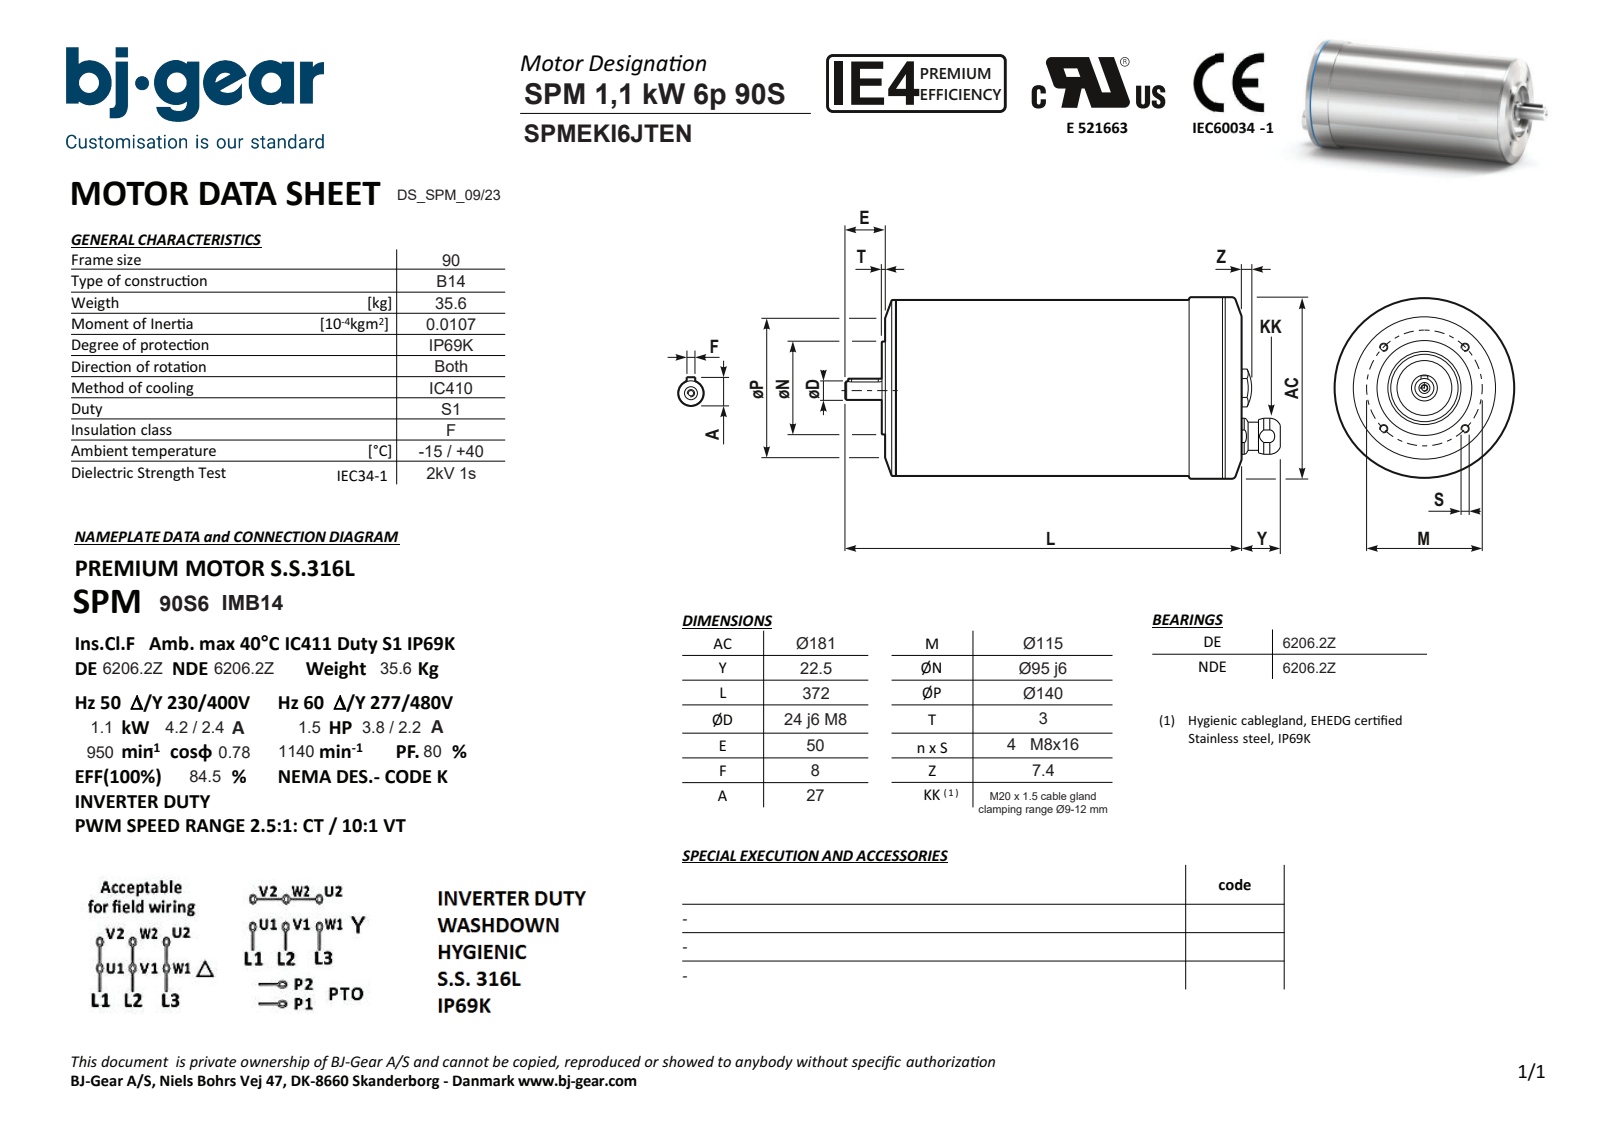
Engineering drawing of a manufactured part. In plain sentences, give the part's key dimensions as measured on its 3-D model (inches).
The part is named "SPMEKI6JTENN4KSA1-N---NNN". Its 3-D file was written by "Solid Edge (AUTOMOTIVE_DESIGN)". It is 1 solid with 87 faces: 30 planar, 32 cylindrical and 25 other. Overall it measures 15.728 by 7.126 by 7.126 inches. Its volume is 489 cubic inches and its surface area 369.9 square inches. Round holes: 4 of diameter 0.262, 1 of diameter 0.194, 1 of diameter 0.276, 1 of diameter 0.331, 1 of diameter 0.528, 1 of diameter 3.346. Round bosses or shafts: 1 of diameter 7.126, 1 of diameter 7.125, 1 of diameter 7.008, 1 of diameter 7.007, 1 of diameter 3.74, 1 of diameter 1.181, 1 of diameter 0.945, 1 of diameter 0.787. Partial cylindrical surfaces (rounded edges, fillets, slot ends): 2 of radius 0.157, 1 of radius 0.504. The main face-to-face distances are 12.677, 0.236, 12.441, 12.795, 0.354, 0.118, 0.315, 0.945, 1.969, 14.646. The hole center spacings are 2.264, 3.202, 1.697, 4.092, 4.528, 2.165.
